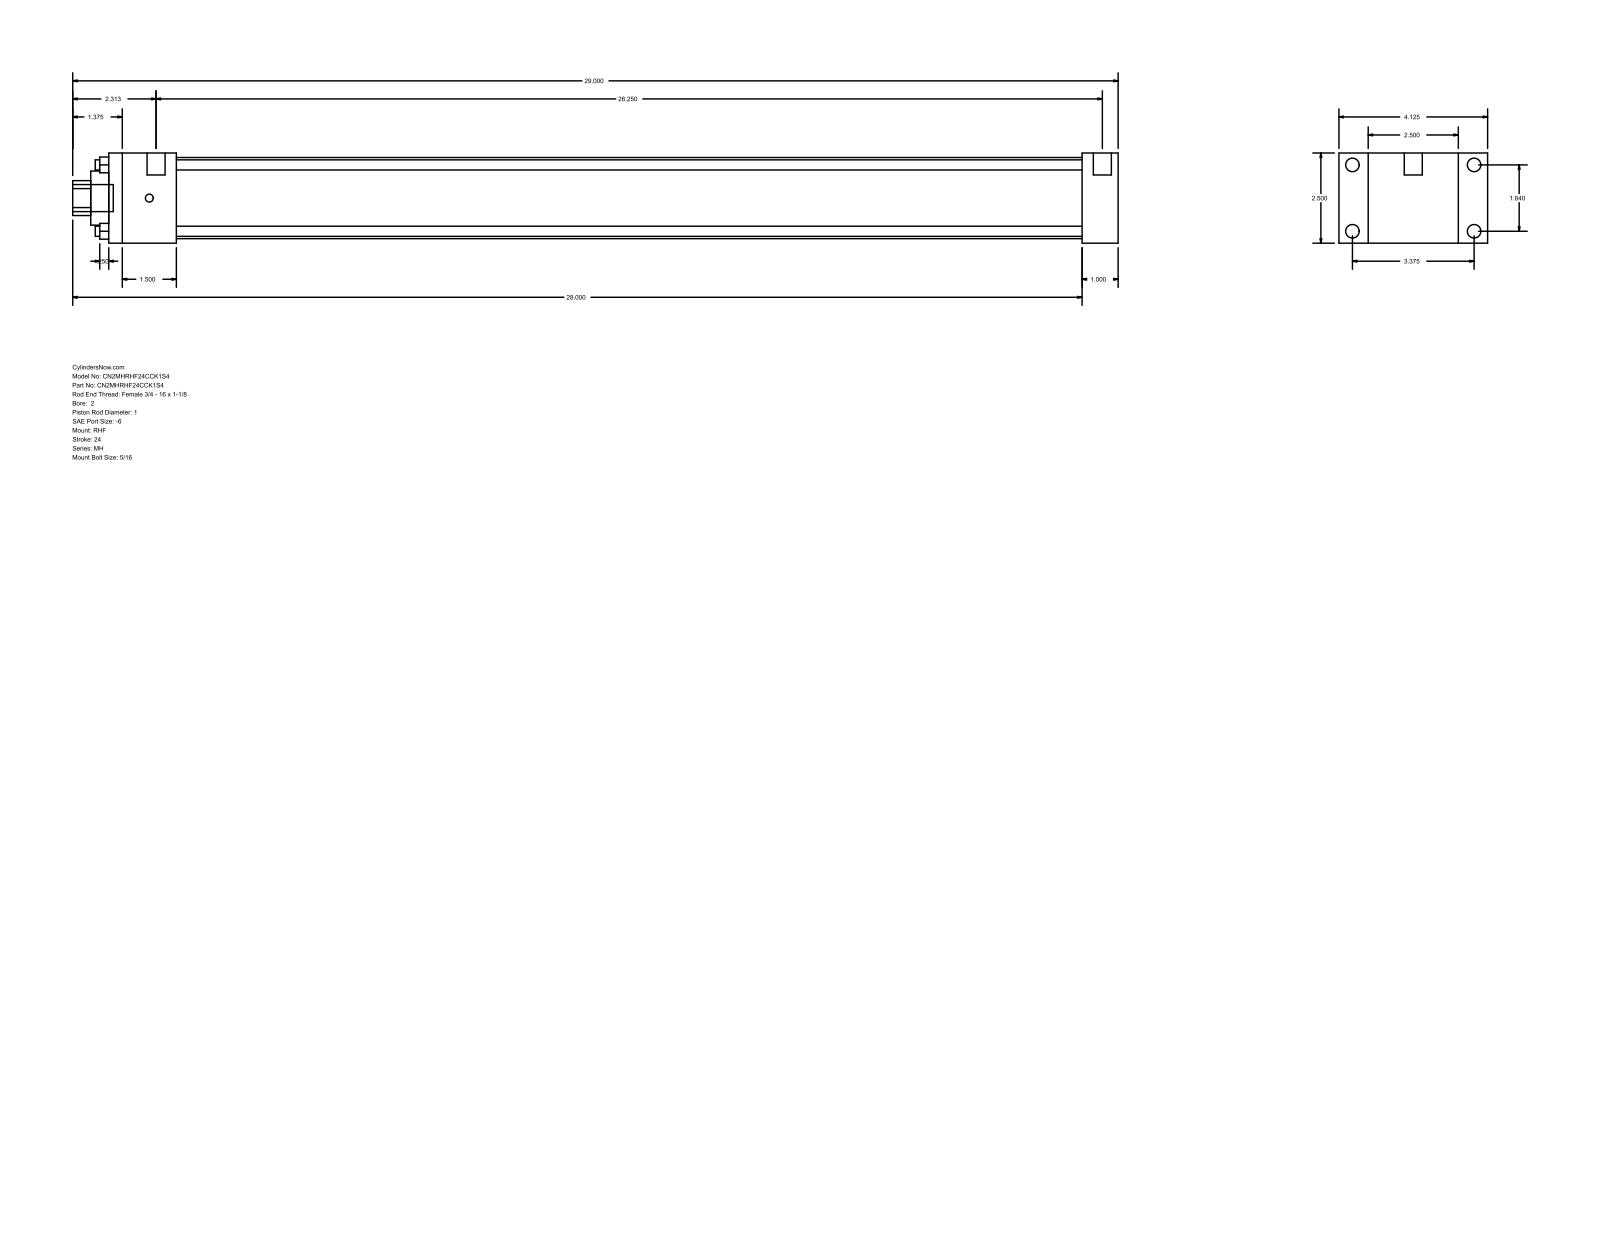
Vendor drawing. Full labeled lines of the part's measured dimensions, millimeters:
Part name (STEP PRODUCT): MH_RHF__0200_1
STEP written by: GSSL Pune (CONFIG_CONTROL_DESIGN)
Units: millimetres
Bodies: 0 solids, 88 faces (60 planar, 28 cylindrical, 0 other)
Overall size (bounding box): 736.6 × 104.78 × 63.5
Round holes (diameter × count): ⌀7.14 ×4, ⌀25.4 ×1, ⌀38.1 ×1, ⌀57.15 ×1
Round bosses / shafts (diameter × count): ⌀9.53 ×4, ⌀5.56 ×4, ⌀12.7 ×2, ⌀19.05 ×1
Partial cylindrical surfaces — rounded edges, fillets, slot ends (radius × count): R12.29 ×1
Main face-to-face distances: 63.5, 25.4, 20.64, 84.14, 711.2, 685.8, 104.78, 47.63, 638.17, 663.57
Hole centre spacings: 33.05, 46.74, 66.1
